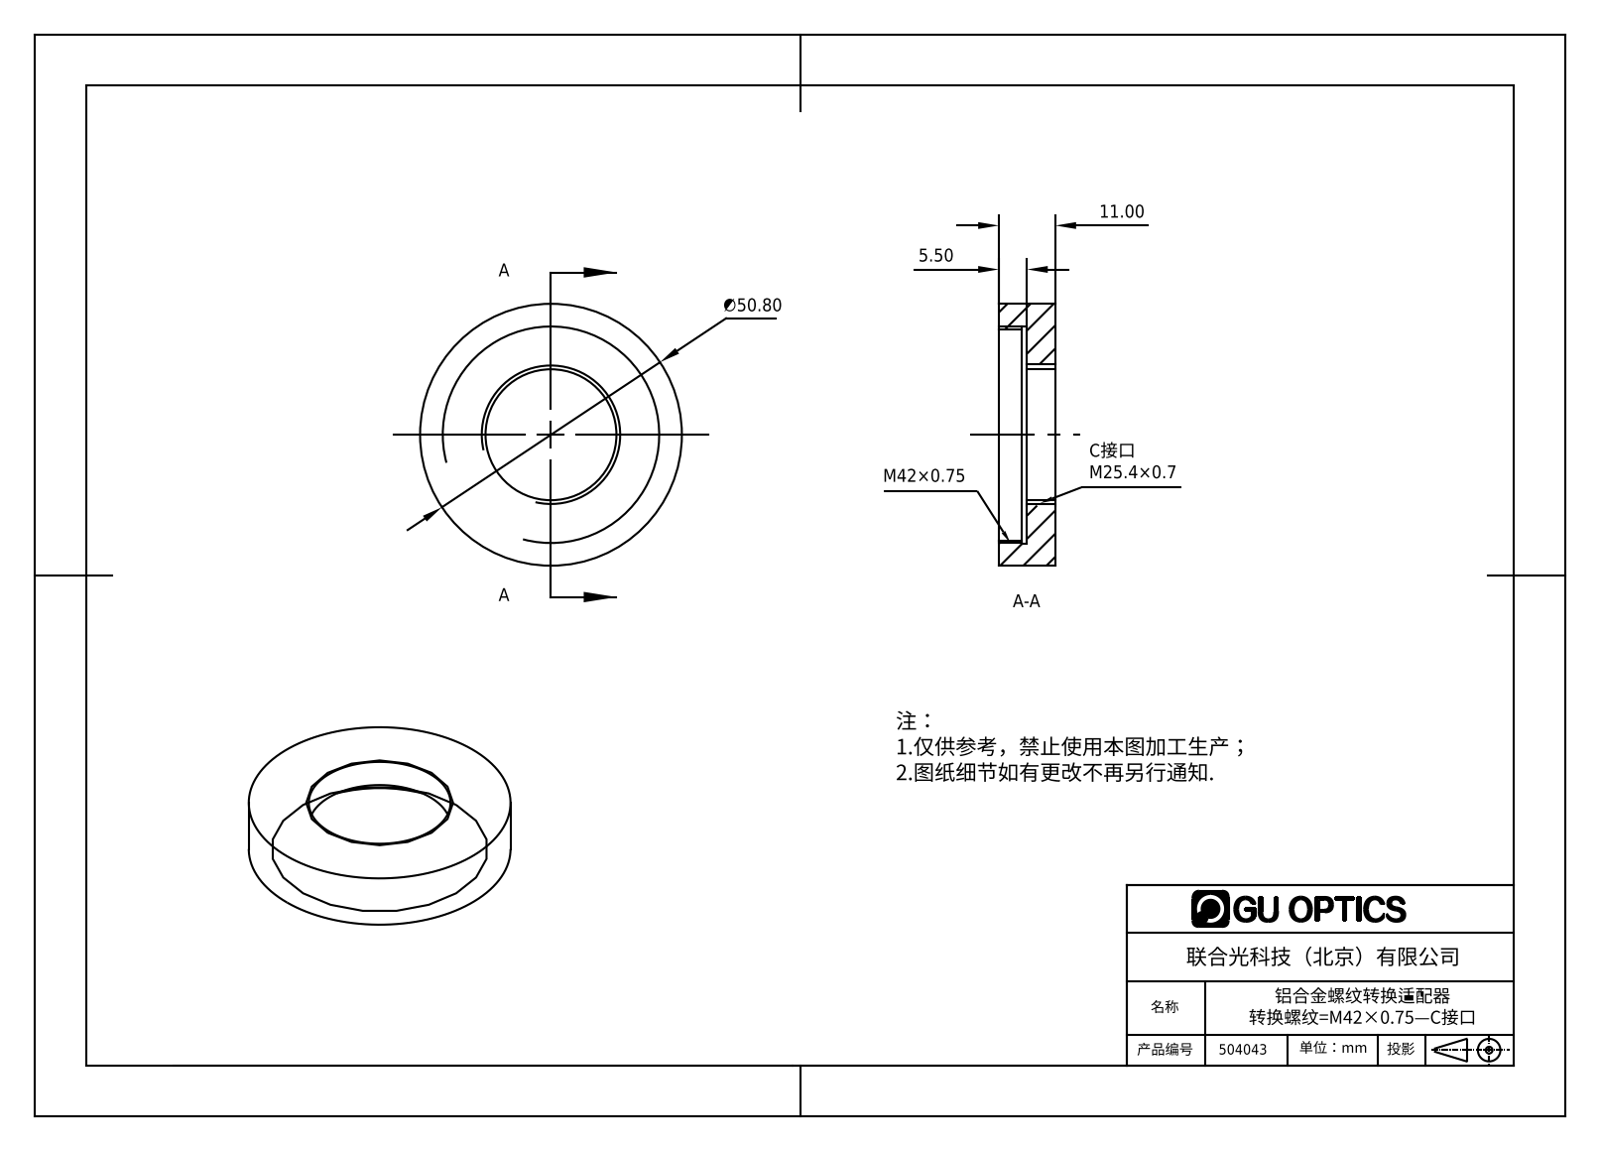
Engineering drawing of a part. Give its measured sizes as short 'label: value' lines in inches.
name: 504043
written by: SolidWorks 2020 (CONFIG_CONTROL_DESIGN)
unit: in
bodies: 1 solid, 12 faces (4 planar, 8 cylindrical, 0 other)
size: 2 × 2 × 0.433
volume: 0.721 in³; area: 9.494 in²
holes: 1× ⌀1, 1× ⌀1.654, 1× ⌀1.701
bosses: 1× ⌀2
face distances: 0.217, 0.433, 0.177, 0.039, 0.256
